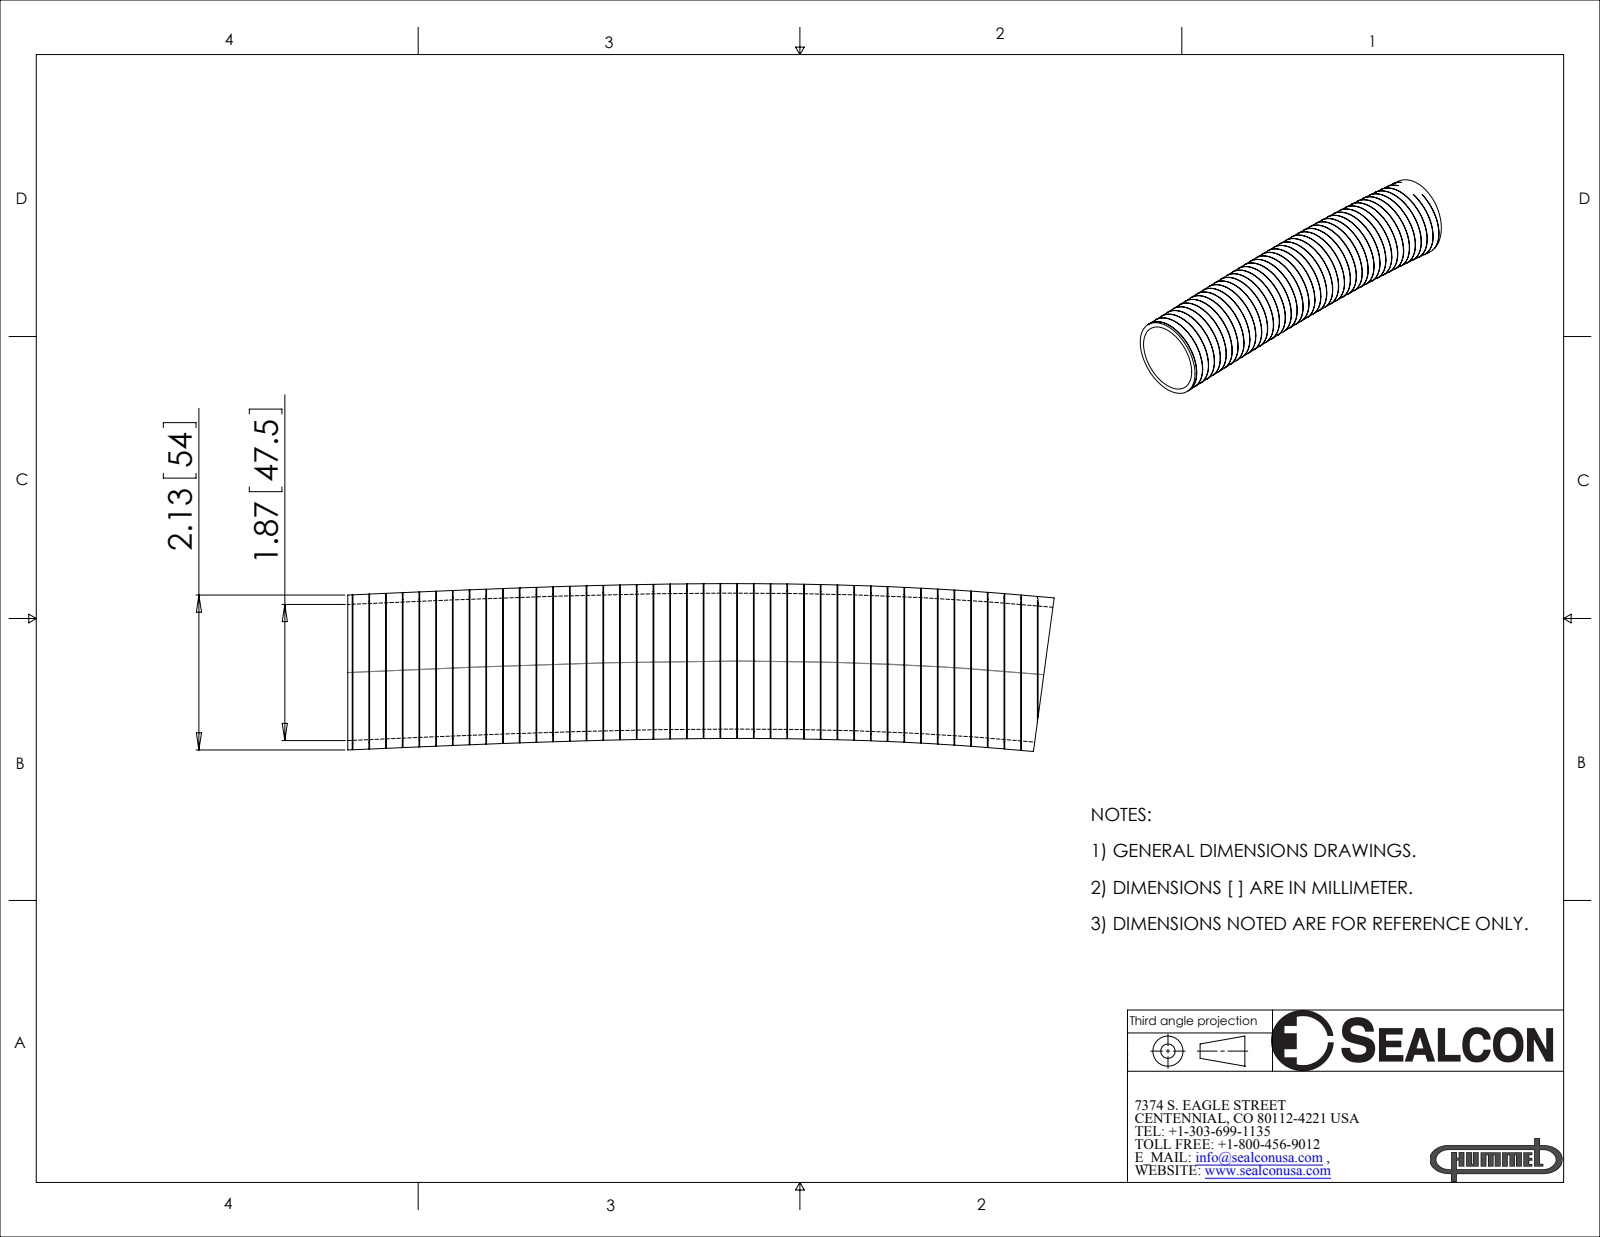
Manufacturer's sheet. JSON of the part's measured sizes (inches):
{"part_name": "SM-1013-HY", "step_written_by": "SolidWorks 2007 (AUTOMOTIVE_DESIGN)", "units": "inches", "bodies": {"solids": 1, "faces": 259, "planar": 86, "cylindrical": 86, "other": 87}, "overall_size": [9.713, 2.307, 2.13], "volume_in3": 7.562, "surface_area_in2": 172.4, "round_bosses_or_shafts": [[1.94, 39]], "partial_cylinders_radius": [[1.07, 3], [0.97, 1]], "face_to_face_distances": [0.23, 0.23, 0.229, 0.459, 0.239, 0.219, 0.688, 0.22, 7.126, 0.689]}
